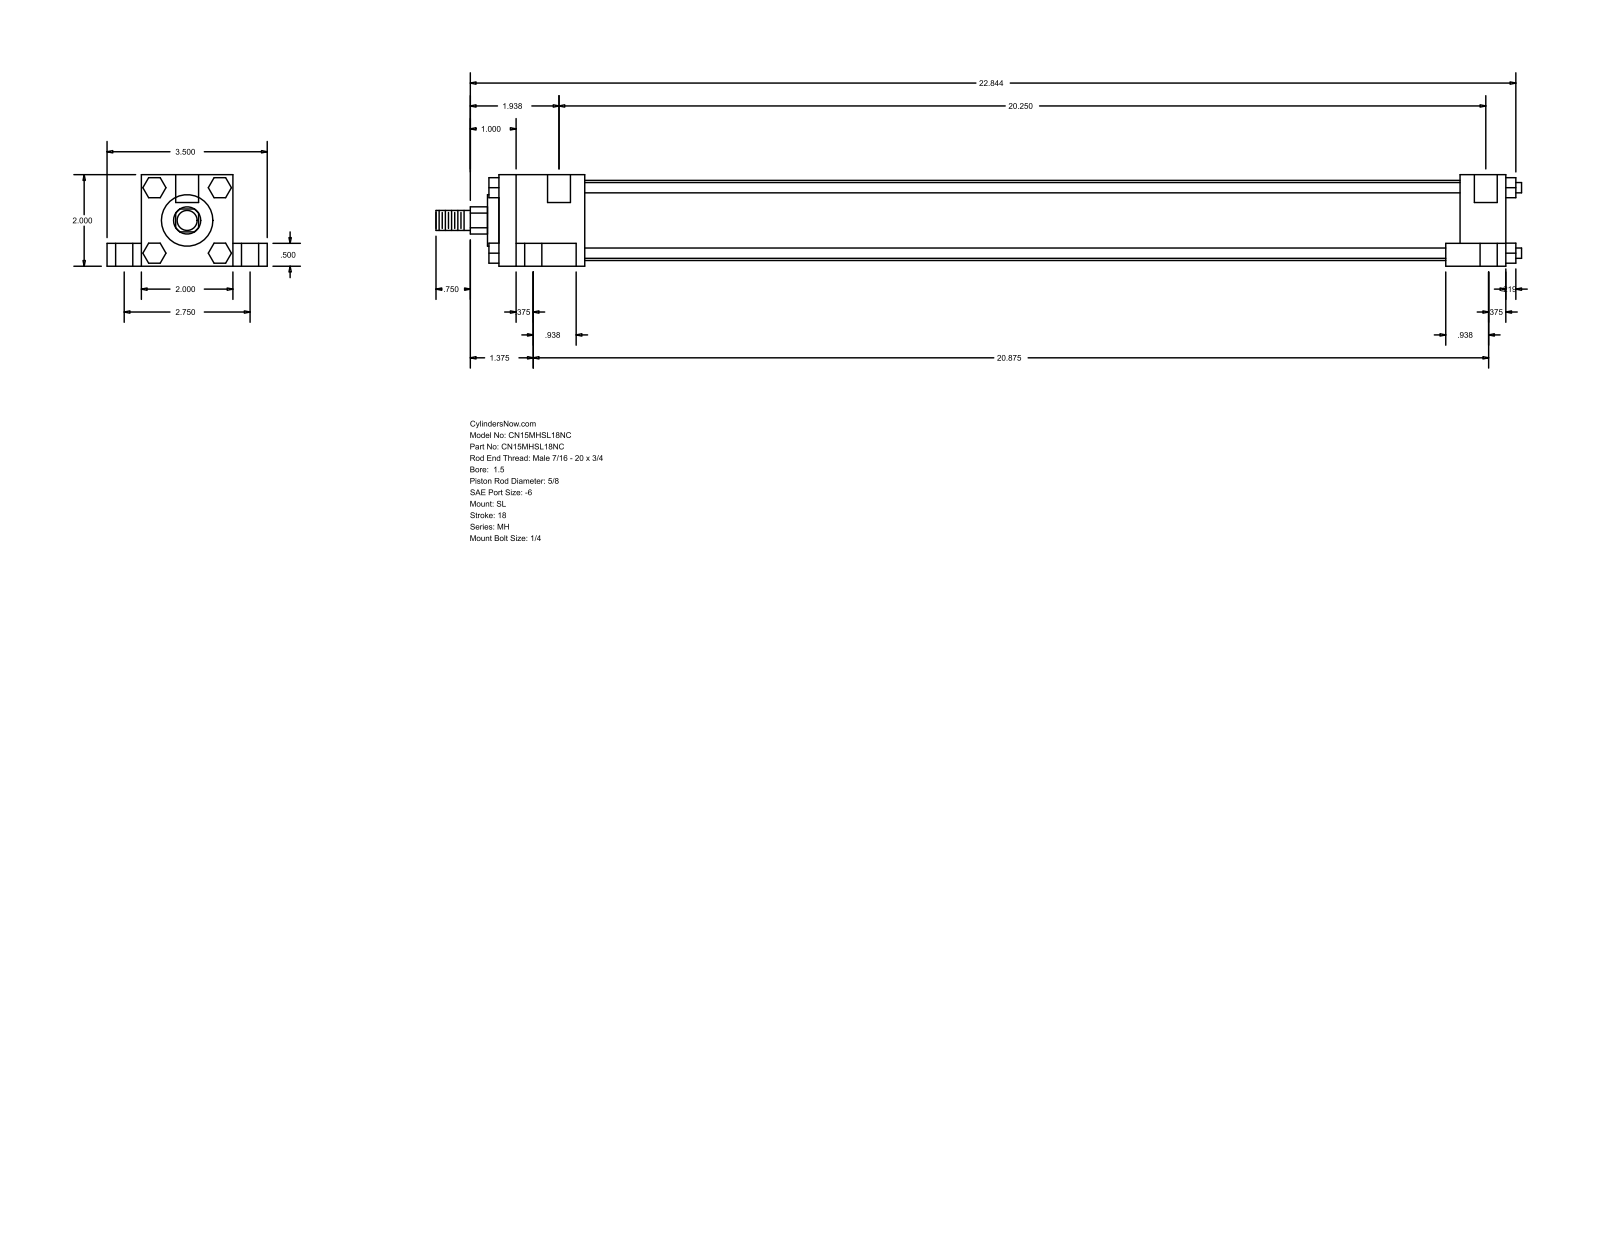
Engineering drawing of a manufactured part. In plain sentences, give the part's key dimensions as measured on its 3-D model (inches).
The part is named "MH_SL__0150_0.625". Its 3-D file was written by "GSSL Pune (CONFIG_CONTROL_DESIGN)". It is 0 solids with 148 faces: 112 planar, 36 cylindrical and 0 other. Overall it measures 23.719 by 3.5 by 2 inches. Round holes: 4 of diameter 0.219, 4 of diameter 0.375, 4 of diameter 0.625, 2 of diameter 0.5. Round bosses or shafts: 4 of diameter 0.225, 1 of diameter 1.75, 1 of diameter 1.125, 1 of diameter 0.625, 1 of diameter 0.437. Partial cylindrical surfaces (rounded edges, fillets, slot ends): 1 of radius 0.297. The main face-to-face distances are 2, 1.5, 0.75, 0.5, 2.75, 22, 1, 0.375, 21, 1.875. The hole center spacings are 1.376, 1.443, 1.485, 2.75, 20.359, 20.375, 20.483, 20.858.
